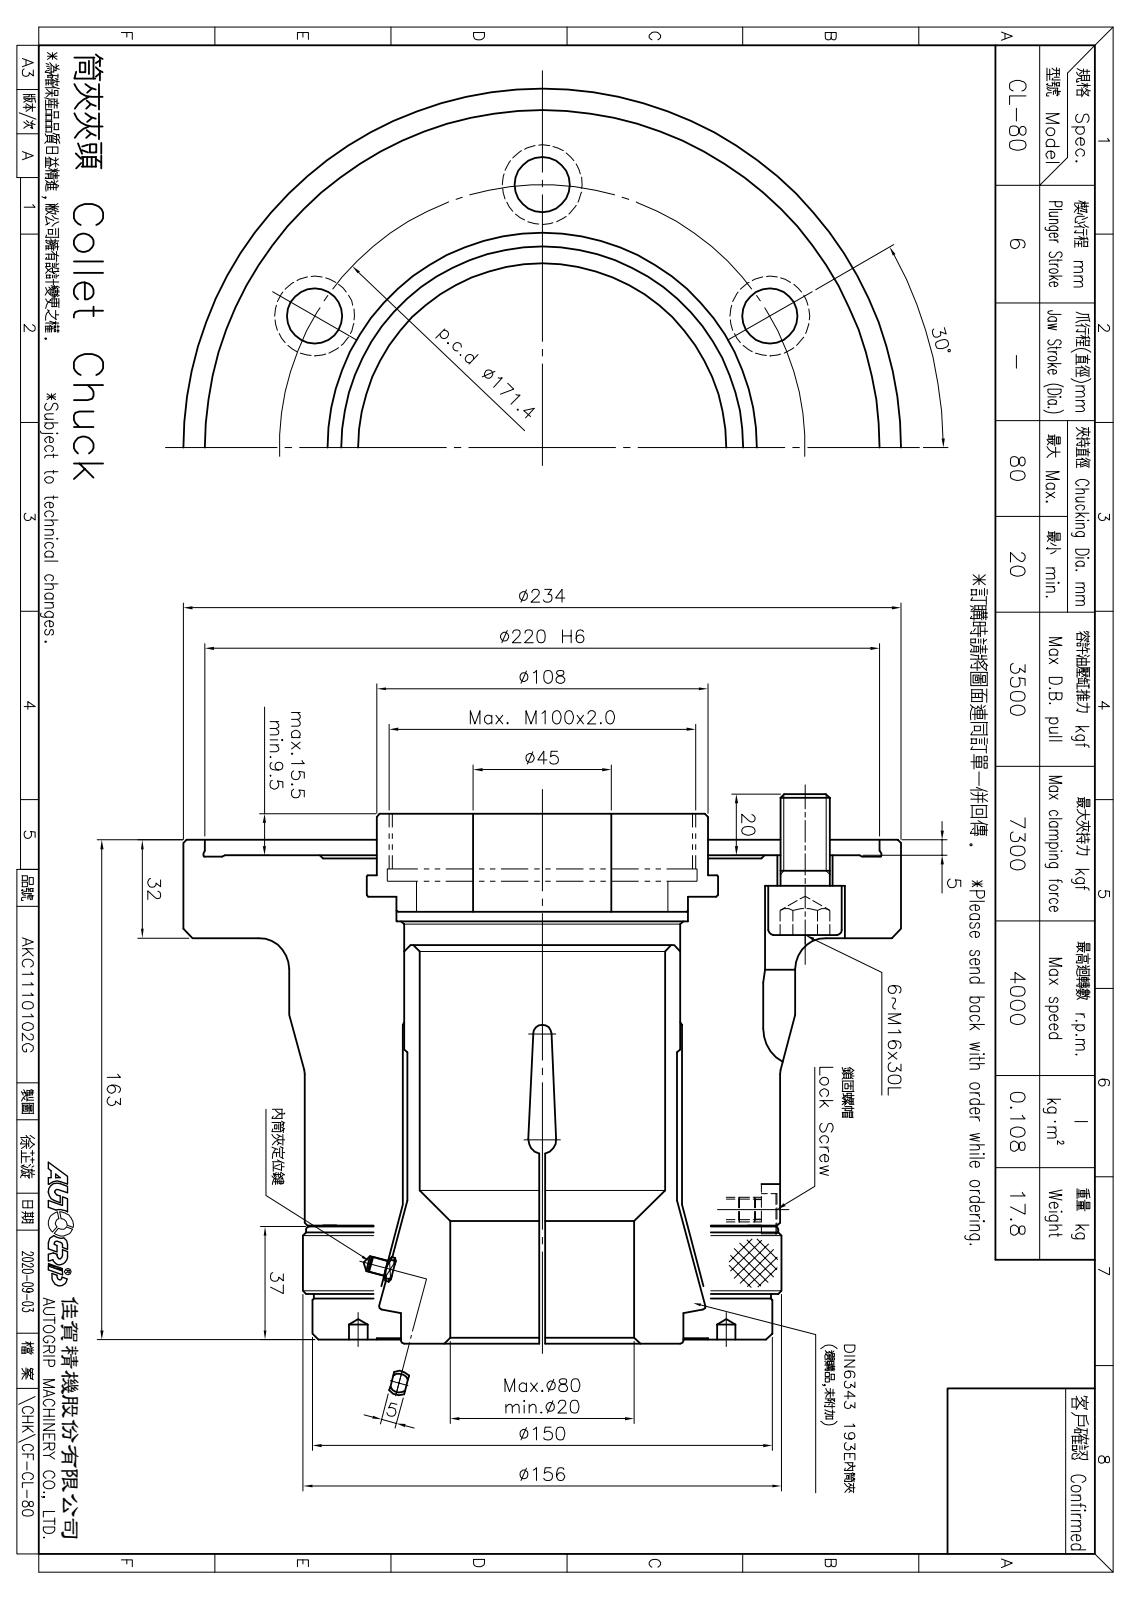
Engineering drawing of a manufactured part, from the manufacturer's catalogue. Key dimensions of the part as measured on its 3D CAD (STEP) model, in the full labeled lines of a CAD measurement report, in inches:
Part name (STEP PRODUCT): FSW320300; 圓頭內六角螺栓_M16x30; CF-CL-42-08000; CF-CL-80-01010 (+4 more)
STEP written by: SolidWorks 2016 (CONFIG_CONTROL_DESIGN)
Units: inches
Bodies: 12 solids, 448 faces (164 planar, 151 cylindrical, 133 other)
Overall size (bounding box): 9.213 × 9.213 × 7
Volume: 158.4 in³ · Surface area: 663.1 in²
Round holes (diameter × count): ⌀0.709 ×6, ⌀1.024 ×6, ⌀0.236 ×2, ⌀0.197 ×1, ⌀0.268 ×1, ⌀3.228 ×1, ⌀3.543 ×1, ⌀3.583 ×1, ⌀3.74 ×1, ⌀3.858 ×1, ⌀3.976 ×1, ⌀4.665 ×1
Round bosses / shafts (diameter × count): ⌀0.945 ×6, ⌀0.63 ×6, ⌀9.213 ×1, ⌀6.142 ×1, ⌀6.102 ×1, ⌀6.063 ×1, ⌀5.906 ×1, ⌀5.866 ×1
Partial cylindrical surfaces — rounded edges, fillets, slot ends (radius × count): R0.492 ×24, R0.335 ×3, R0.157 ×1, R0.315 ×1, R0.325 ×1, R3.248 ×1
Main face-to-face distances: 1.063, 0.453, 5.15, 6.213, 0.61, 0.413, 0.197, 4.756, 3.693, 1.457
Hole centre spacings: 3.374, 5.844, 2.999, 4.993, 6.748, 1.012, 2.362, 5.736
